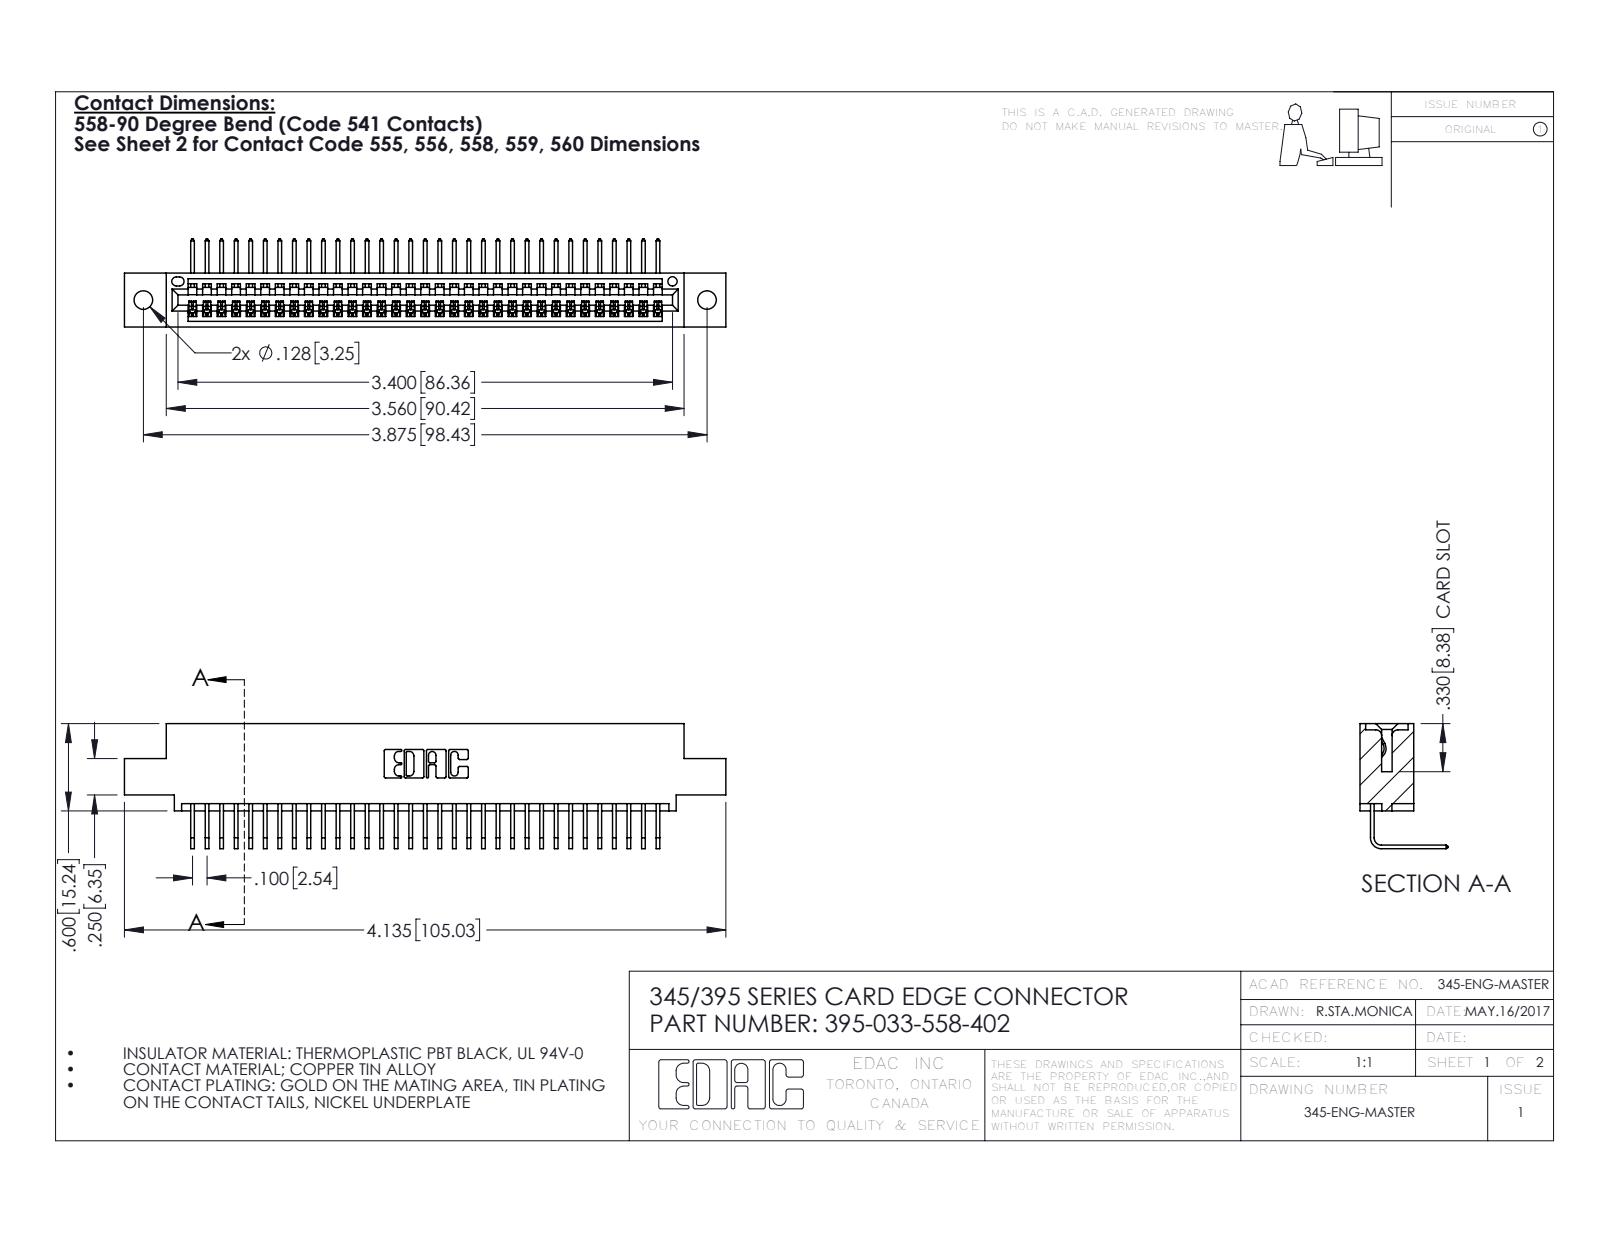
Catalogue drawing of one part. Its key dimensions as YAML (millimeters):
part_name: "345 Part_0.110 Offset - 0.128 Dia; 395-033-558-402; 345-292-001_558 Tail - 2"
step_written_by: "SolidWorks 2016 (CONFIG_CONTROL_DESIGN)"
units: millimeters
bodies: {solids: 34, faces: 2110, planar: 1470, cylindrical: 640, other: 0}
overall_size: [105, 21.8, 15.4]
volume: 9900
surface_area: 13490
round_holes:
  - {diameter: 3.3, count: 2}
  - {diameter: 1.6, count: 1}
partial_cylinders:
  - {radius: 0.2, count: 66}
  - {radius: 0.3, count: 22}
  - {radius: 0.2, count: 6}
  - {radius: 0.8, count: 6}
  - {radius: 0.7, count: 3}
  - {radius: 0.8, count: 2}
  - {radius: 1, count: 2}
  - {radius: 0.4, count: 1}
face_to_face_distances: [1.8, 7.6, 9.4, 5.1, 2.5, 6.9, 0.6, 5.7, 3.8, 1.8]
hole_center_spacings: [6.9, 92.5, 98.4]
